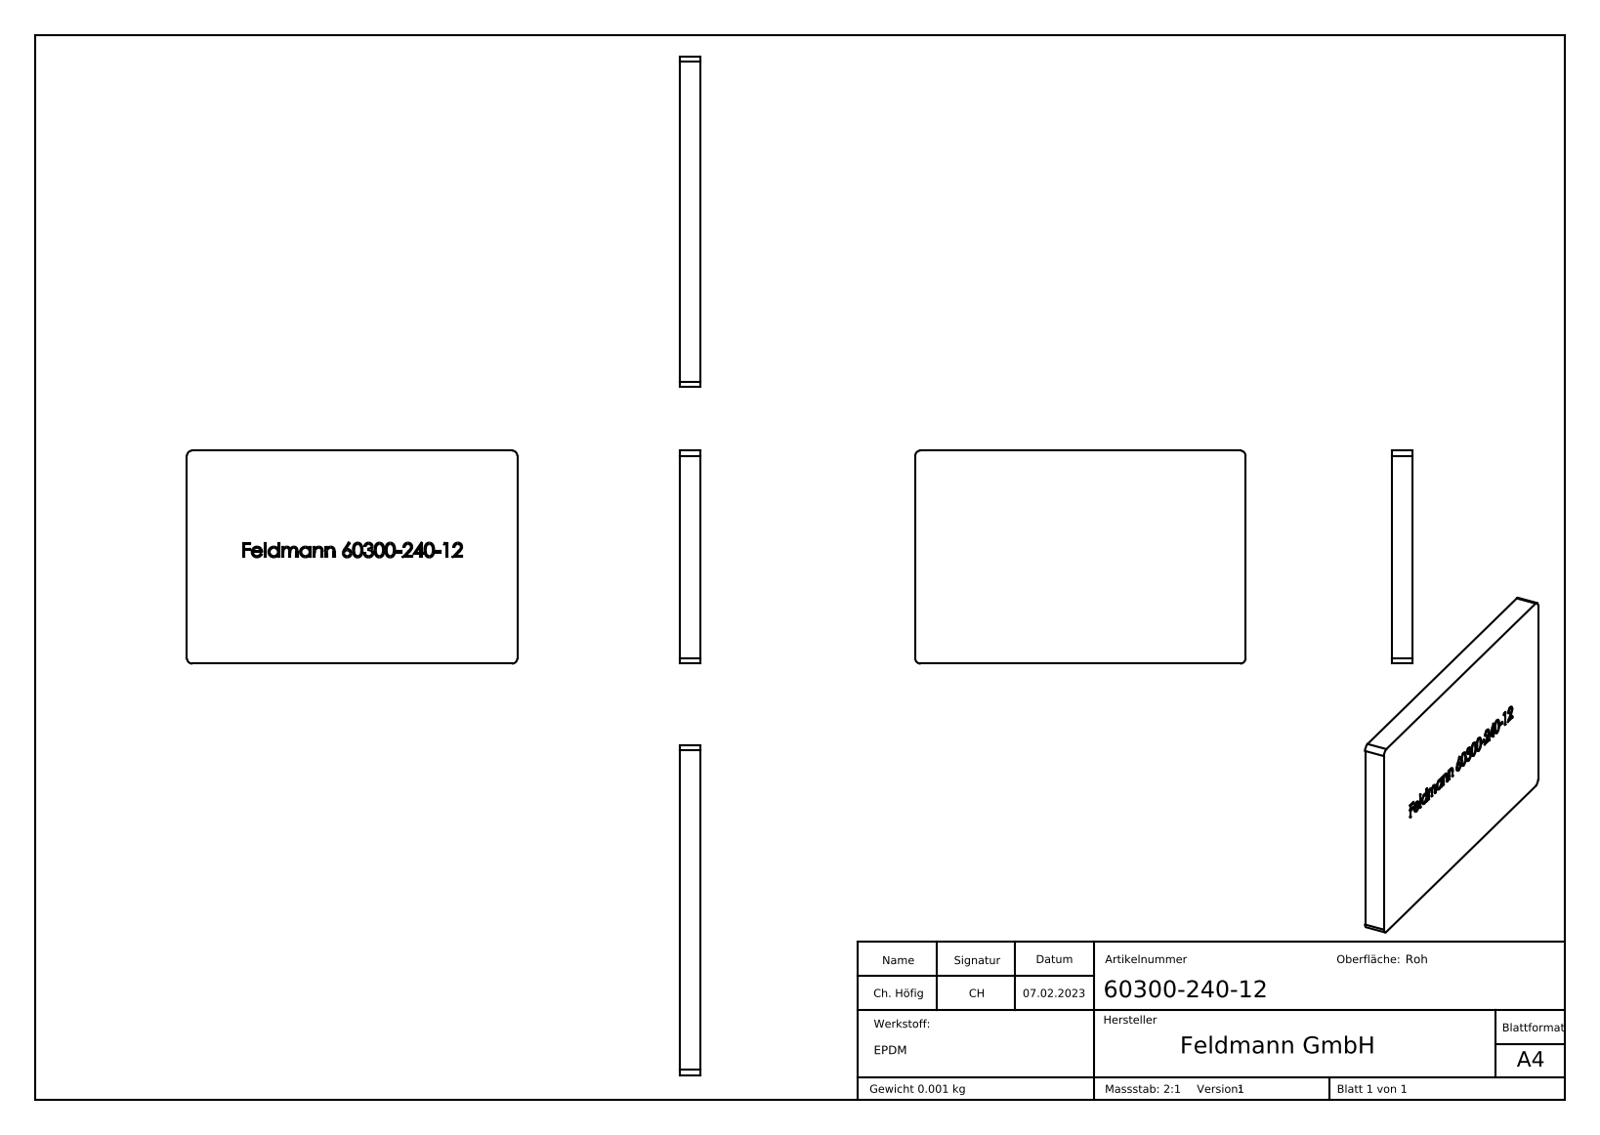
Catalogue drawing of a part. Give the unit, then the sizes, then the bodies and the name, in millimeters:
Units: millimetres
Overall size (bounding box): 31 × 20 × 2
Partial cylindrical surfaces — rounded edges, fillets, slot ends (radius × count): R0.5 ×4
Main face-to-face distances: 2, 20, 31, 1.9, 10, 0.44, 0.39, 17.05, 2.02, 19.07
Volume: 1 239 mm³ · Surface area: 1 453 mm²
Bodies: 1 solid, 257 faces (134 planar, 4 cylindrical, 119 other)
Part name (STEP PRODUCT): 60300-240-12
STEP written by: SolidWorks 2018 (CONFIG_CONTROL_DESIGN)
